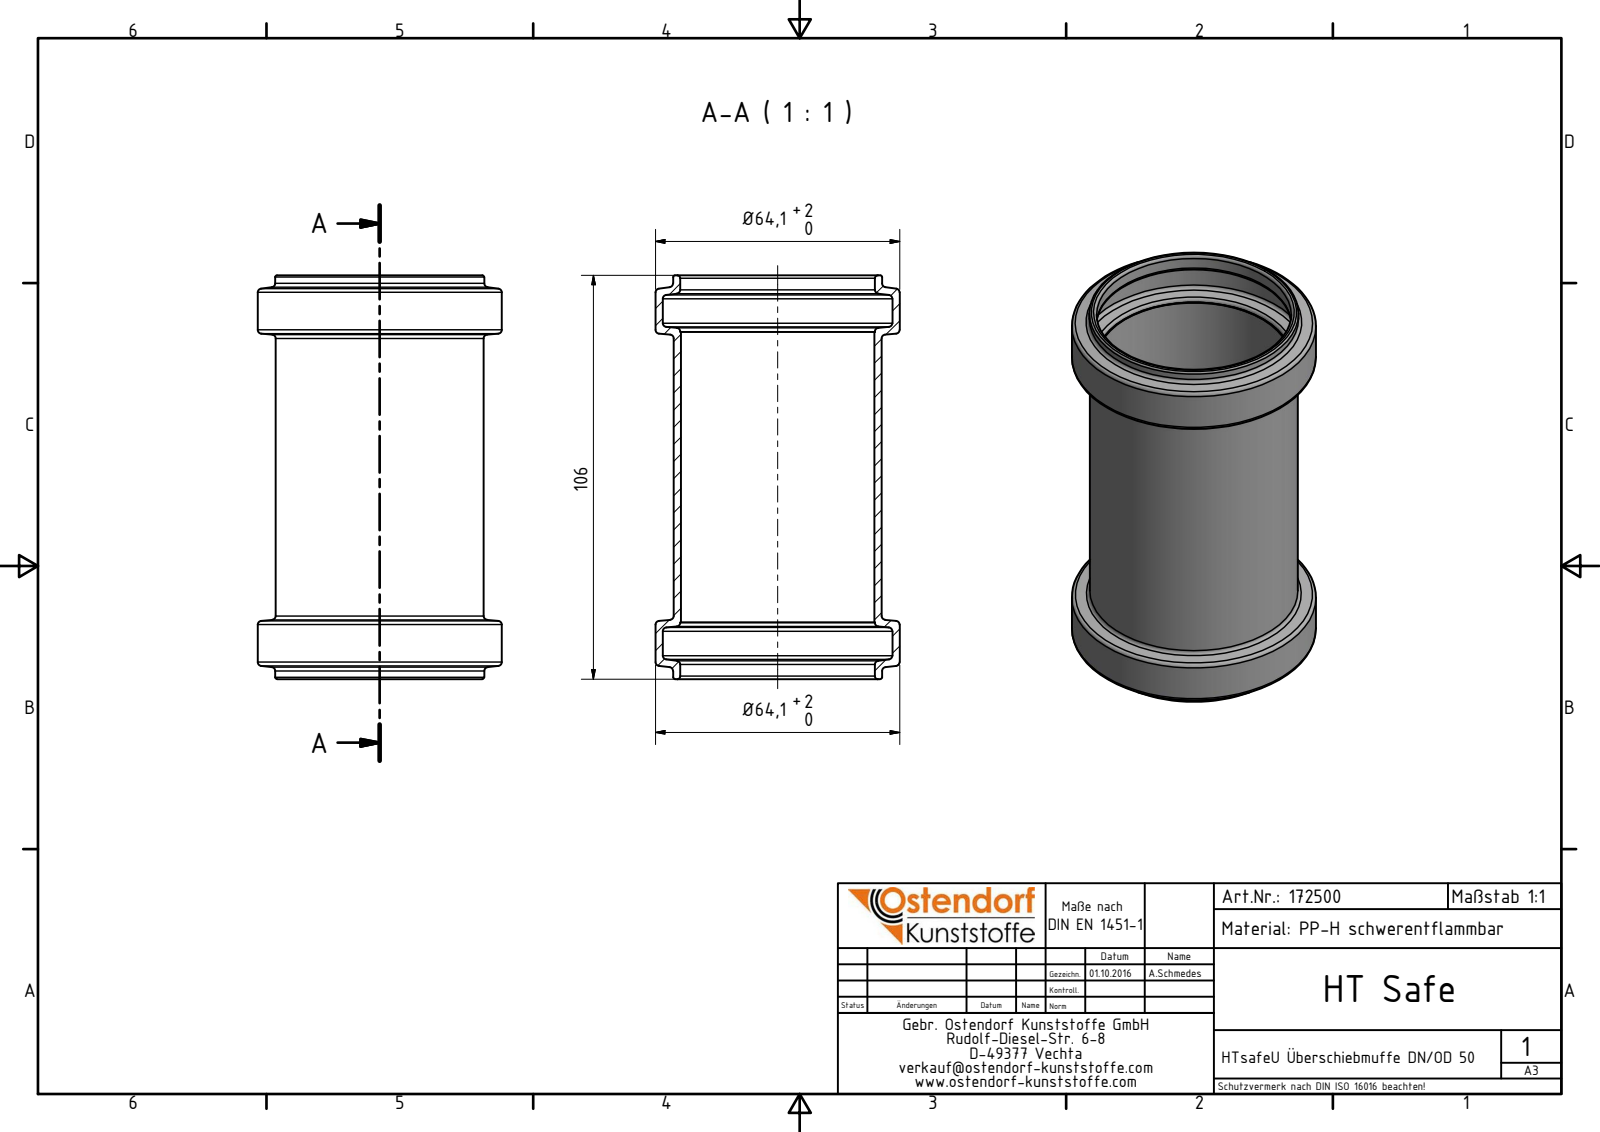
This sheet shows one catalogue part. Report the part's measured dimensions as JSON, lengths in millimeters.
{"part_name": "172500 HTsafeU DN_OD 50", "step_written_by": "Autodesk Inventor 2016 (AUTOMOTIVE_DESIGN)", "units": "millimeters", "bodies": {"solids": 1, "faces": 44, "planar": 4, "cylindrical": 12, "other": 28}, "overall_size": [106, 64.1, 64.1], "volume_mm3": 40213, "surface_area_mm2": 41932, "round_holes": [[50.8, 1], [51.1, 1], [60.3, 1]], "round_bosses_or_shafts": [[64.1, 1], [54.9, 1], [54.6, 1]], "face_to_face_distances": [106, 14.9, 91.1, 76.2]}
